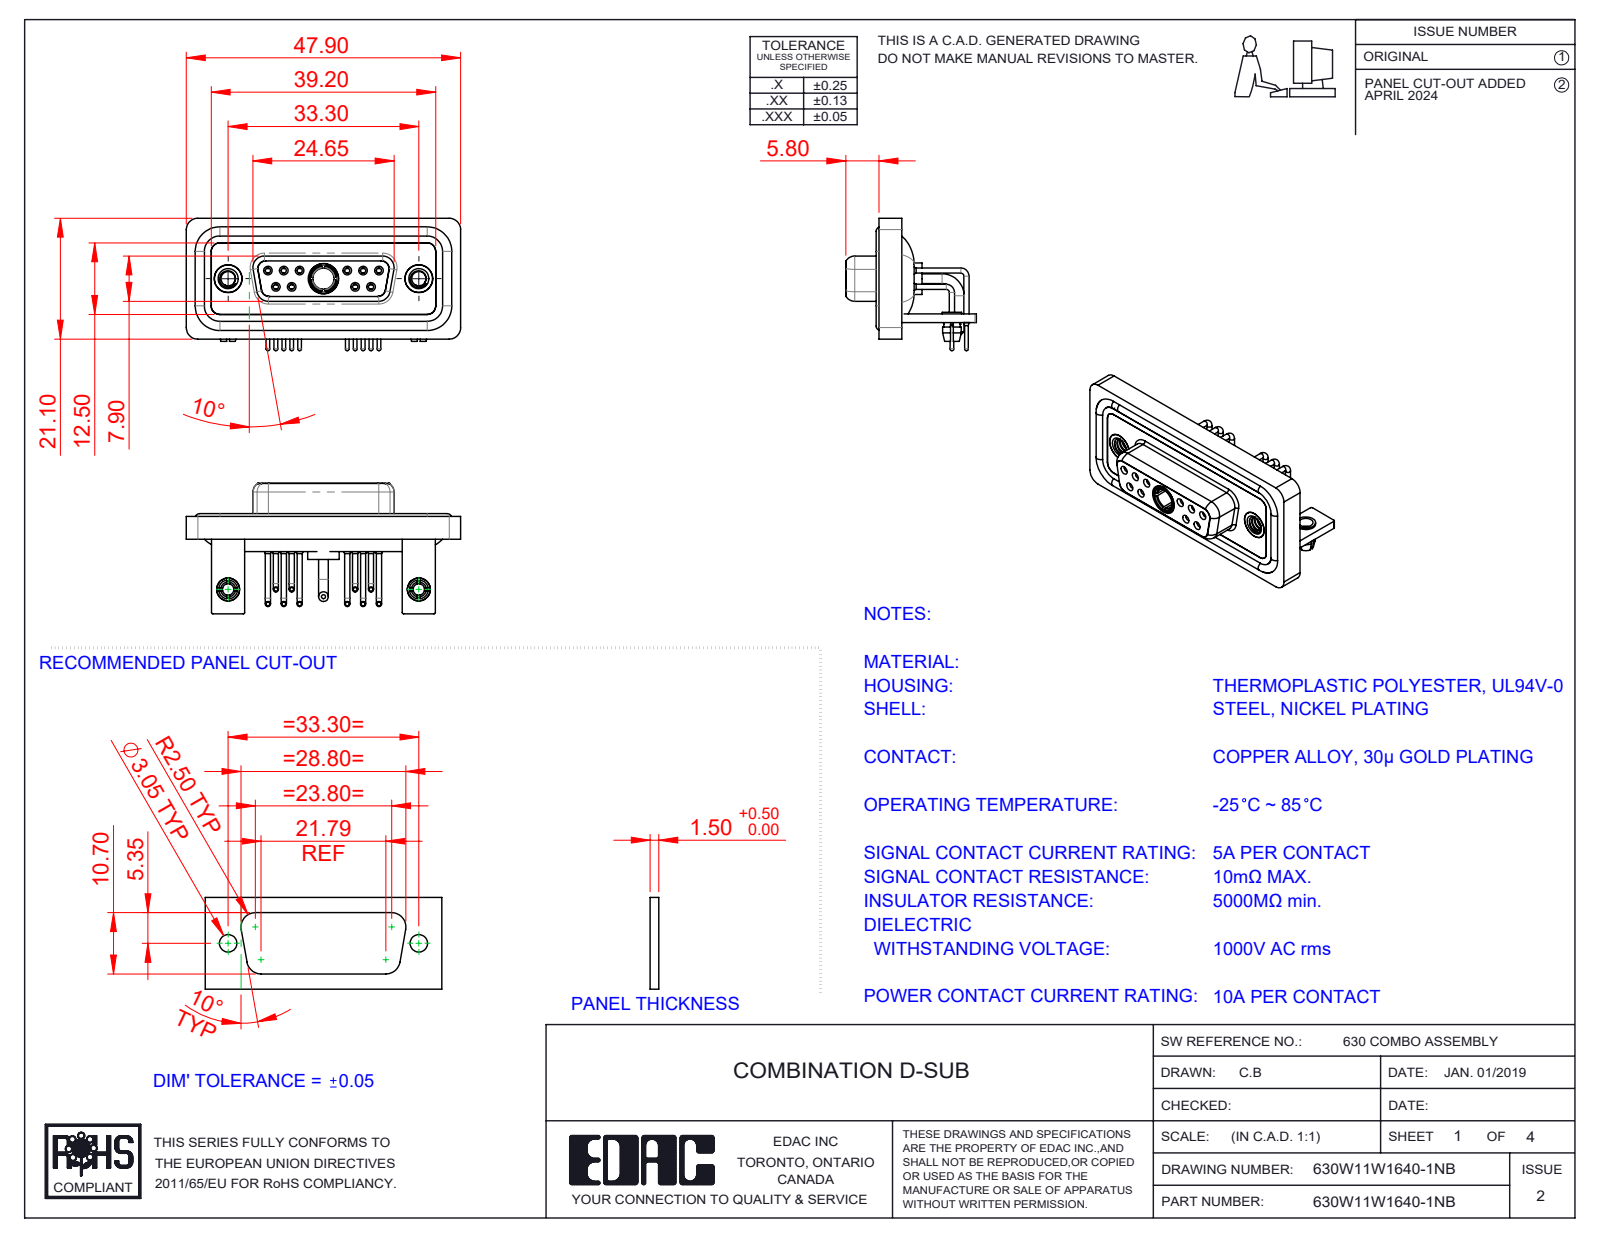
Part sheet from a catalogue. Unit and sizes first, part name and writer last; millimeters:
Units: millimetres
Overall size (bounding box): 47.9 × 23.12 × 22.8
Round holes (diameter × count): ⌀2 ×12, ⌀0.9 ×10, ⌀1.1 ×10, ⌀1.5 ×10, ⌀1.7 ×6, ⌀1.6 ×4, ⌀2.5 ×4, ⌀4.85 ×3, ⌀3.2 ×2, ⌀4 ×2, ⌀4.05 ×2, ⌀5 ×2
Round bosses / shafts (diameter × count): ⌀1.6 ×10, ⌀0.9 ×10, ⌀0.65 ×10, ⌀4.95 ×2, ⌀4.8 ×2, ⌀4 ×2, ⌀3.4 ×2, ⌀3.3 ×2
Partial cylindrical surfaces — rounded edges, fillets, slot ends (radius × count): R2 ×21, R1.5 ×18, R0.25 ×16, R1.35 ×12, R1.6 ×8, R0.5 ×5, R0.6 ×4, R0.65 ×4
Main face-to-face distances: 0.4, 2.9, 1.5, 1.8, 3.7, 1.1, 1.6, 4.1, 0.8, 2.5
Hole centre spacings: 3.16, 2.77, 13.85, 11.08, 16.62, 5.03, 5.04, 5.54
Volume: 6 555 mm³ · Surface area: 11 369 mm²
Bodies: 23 solids, 1128 faces (352 planar, 497 cylindrical, 279 other)
Part name (STEP PRODUCT): 630Combo Shell Rear_15 Contacts; 630Combo Threaded Rivet_A; 630Combo Shell Front_15 Contacts; 630Combo Contact Row 1_50 Contacts (+7 more)
STEP written by: SolidWorks 2023 (CONFIG_CONTROL_DESIGN)
